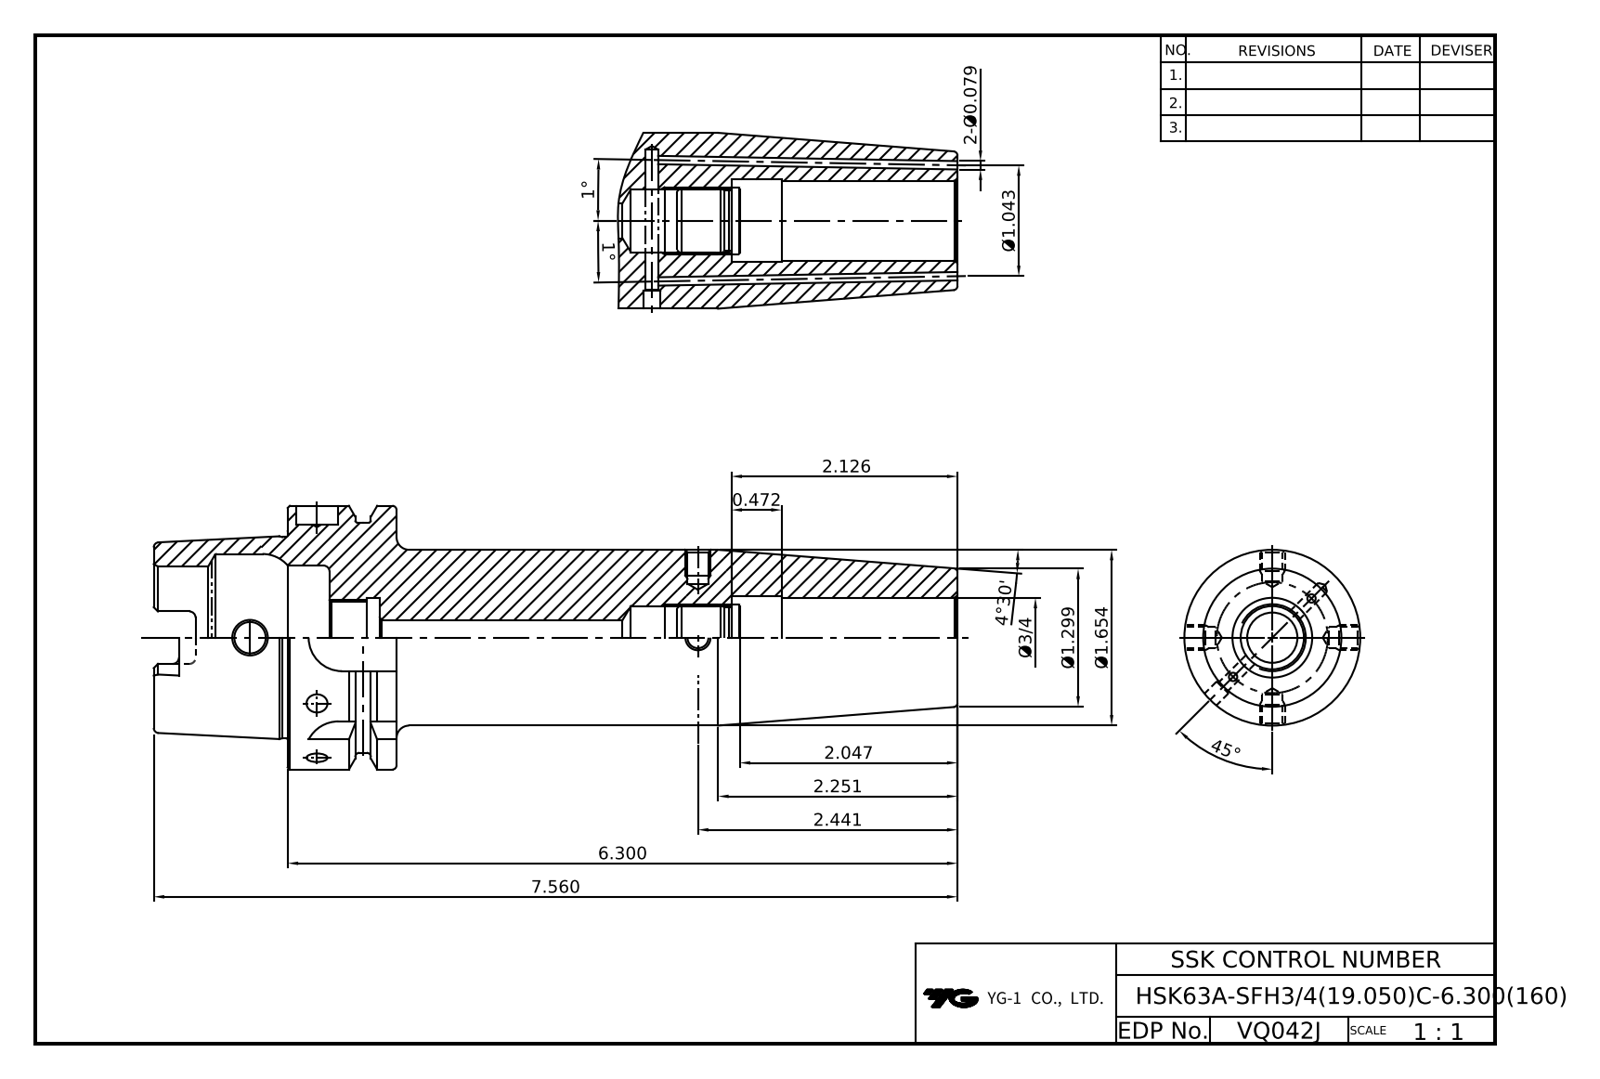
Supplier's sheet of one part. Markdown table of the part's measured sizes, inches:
| quantity | value |
| --- | --- |
| part name | HSK63A_BALANCE_20200217 |
| STEP written by | CREO PARAMETRIC BY PTC INC, 2018500 (CONFIG_CONTROL_DESIGN) |
| units | inches |
| bodies | 1 solid, 184 faces (57 planar, 57 cylindrical, 70 other) |
| overall size | 7.559 × 2.48 × 2.48 |
| volume | 13.94 in³ |
| surface area | 71.21 in² |
| round holes (diameter × count) | 0.197 × 2, 0.295 × 1, 0.331 × 1, 0.394 × 1, 0.591 × 1, 0.63 × 1, 0.669 × 1, 0.709 × 1, 0.748 × 1, 0.75 × 1, 0.774 × 1, 1.339 × 1 |
| round bosses / shafts (diameter × count) | 2.48 × 1, 2.165 × 1, 1.891 × 1, 1.654 × 1 |
| partial cylindrical surfaces (radius × count) | 0.059 × 6, 0.113 × 4, 0.315 × 4 |
| main face-to-face distances | 1.024, 0.394, 0.63, 1.26, 5.906, 6.299, 5.276, 1.654, 0.241, 0.389 |
